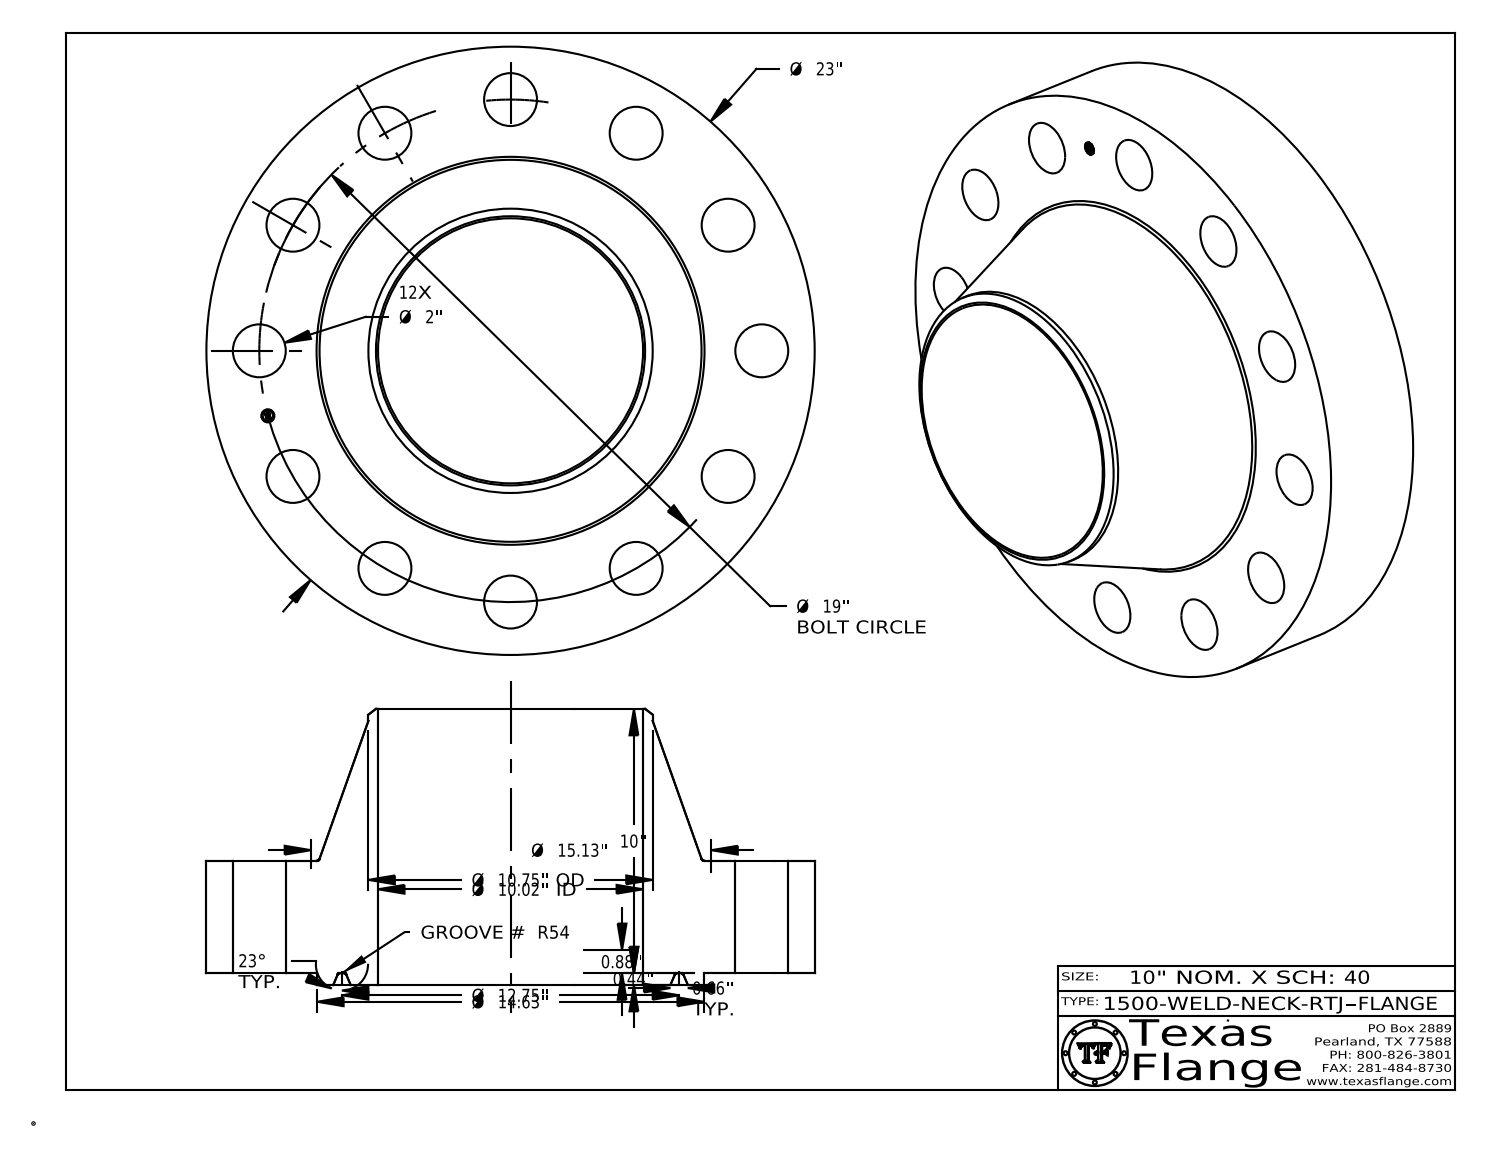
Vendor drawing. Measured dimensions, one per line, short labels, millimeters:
name: 1500-WELD-NECK-RTJ
written by: CATIA V5 STEP AP214 (AUTOMOTIVE_DESIGN)
unit: mm
bodies: 1 solid, 437 faces (371 planar, 52 cylindrical, 14 other)
size: 584.2 × 584.2 × 265.1
volume: 25 500 000 mm³; area: 1 132 000 mm²
holes: 12× ⌀50.8, 1× ⌀12.6, 1× ⌀254.5
bosses: 8× ⌀0.8, 1× ⌀584.2, 1× ⌀371.5, 1× ⌀273.1, 1× ⌀9.9
face distances: 108, 11.1, 119.1, 265.1, 254, 146.1, 118.7, 107.6, 0.4, 146.4
hole spacings: 241.3, 341.2, 417.9, 466.1, 124.9, 482.6, 124.9, 382.9
